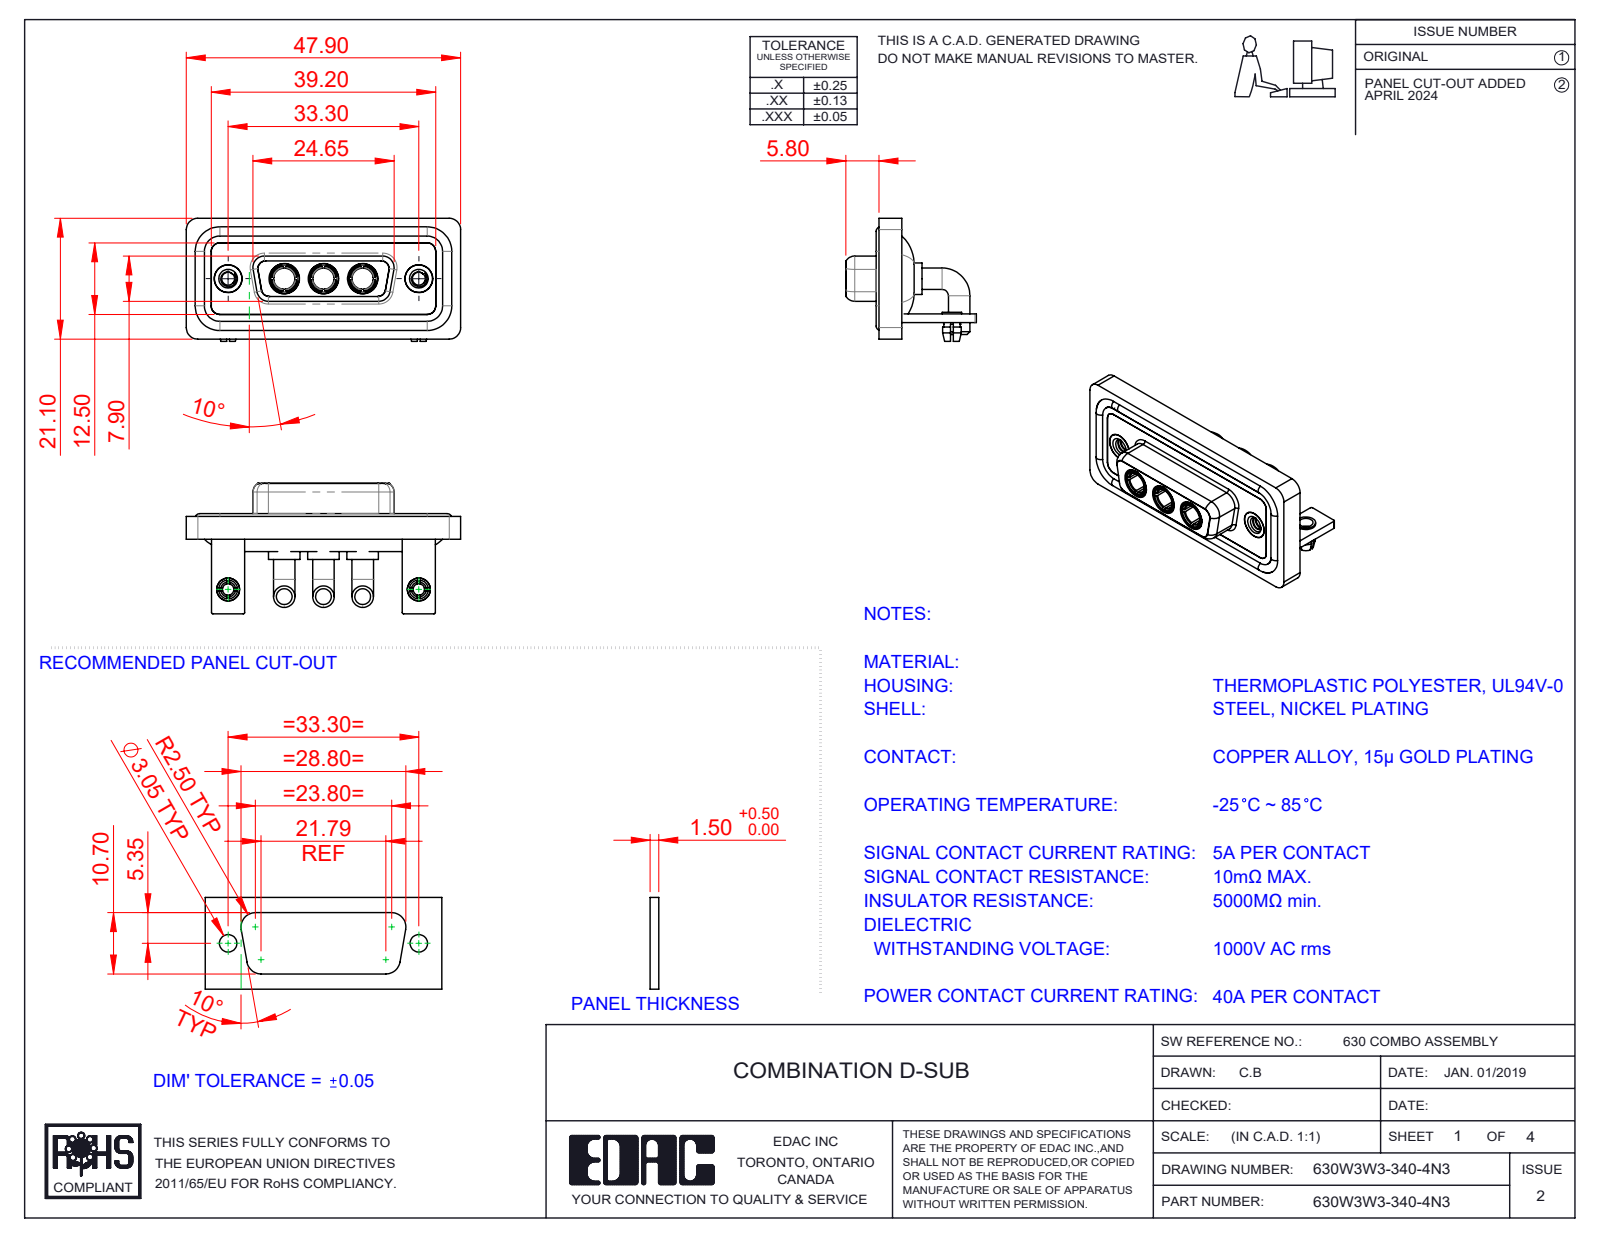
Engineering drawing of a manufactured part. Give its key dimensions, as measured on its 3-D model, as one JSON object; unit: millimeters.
{"part_name": "630Combo Shell Rear_15 Contacts; 630Combo Housing_3W3; 630Combo Waterproof Housing_15 Contacts; 630Combo Stabilizer Bracket_50 Contacts (+5 more)", "step_written_by": "SolidWorks 2023 (CONFIG_CONTROL_DESIGN)", "units": "millimeters", "bodies": {"solids": 17, "faces": 760, "planar": 260, "cylindrical": 319, "other": 181}, "overall_size": [47.9, 22.8, 21.5], "volume_mm3": 6801, "surface_area_mm2": 11049, "round_holes": [[4.85, 5], [3.7, 3], [5.3, 3], [2, 2], [2.26, 2], [2.5, 2], [3.2, 2], [4, 2], [4.05, 2], [5, 2]], "round_bosses_or_shafts": [[3.75, 6], [1.6, 4], [5.5, 3], [5.2, 3], [4.96, 3], [4.75, 3], [4.95, 2], [4.8, 2]], "partial_cylinders_radius": [[2, 21], [1.5, 18], [0.25, 16], [1.35, 12], [1.6, 8], [0.5, 5], [0.6, 4], [0.65, 4]], "face_to_face_distances": [0.4, 2.9, 1.5, 1.8, 3.7, 1.1, 4.1, 1.6, 2.5, 1.4], "hole_center_spacings": [6.85, 9.8, 16.65, 23.5, 33.3, 13.7]}
